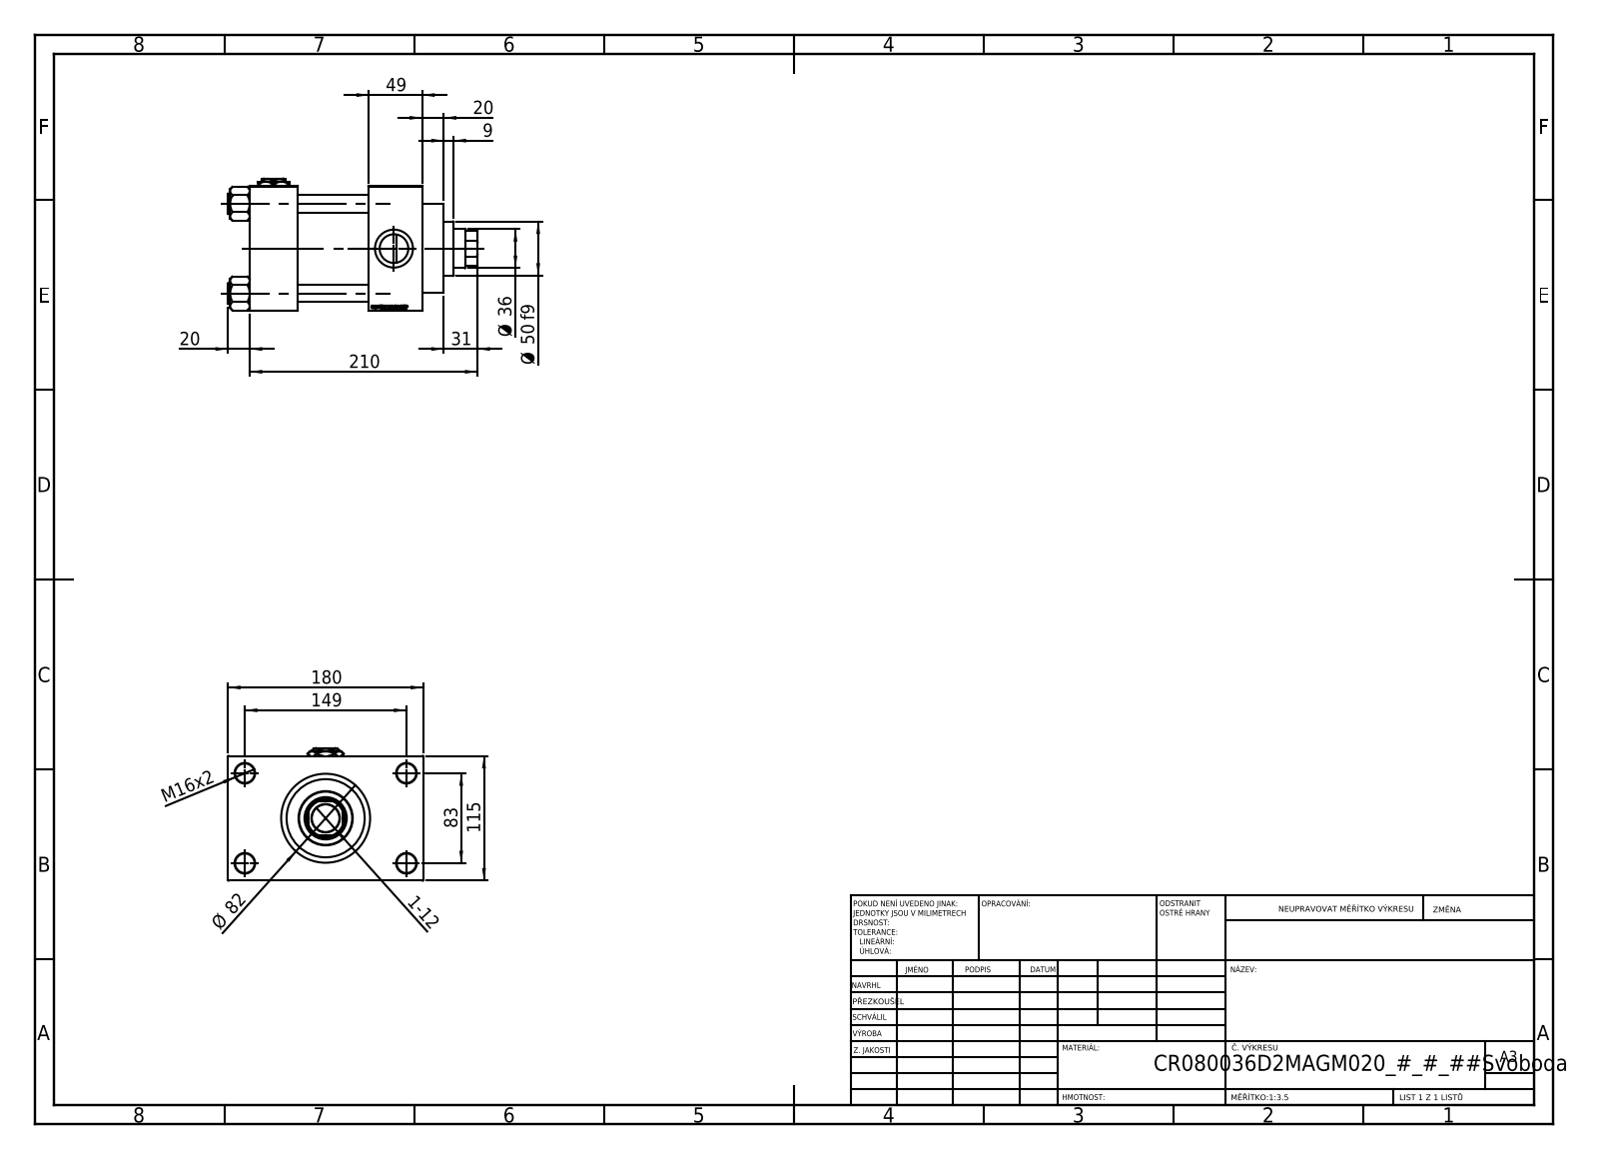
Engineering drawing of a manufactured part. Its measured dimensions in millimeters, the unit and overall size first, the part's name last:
Units: millimetres
Overall size (bounding box): 230 × 180 × 122
Round holes (diameter × count): ⌀16 ×4, ⌀18 ×4, ⌀7 ×2, ⌀26.44 ×2, ⌀35 ×2, ⌀25.5 ×1, ⌀36 ×1, ⌀39 ×1, ⌀61 ×1, ⌀72 ×1, ⌀80 ×1
Round bosses / shafts (diameter × count): ⌀19 ×4, ⌀86 ×1, ⌀82 ×1, ⌀50 ×1
Partial cylindrical surfaces — rounded edges, fillets, slot ends (radius × count): R17.5 ×1
Main face-to-face distances: 115, 66, 110, 49, 44, 159, 32.5, 147.5, 20, 69
Hole centre spacings: 33.15, 58.48, 82.7, 85.28, 89.24, 115.85, 142.43, 83
Volume: 1 983 000 mm³ · Surface area: 298 618 mm²
Bodies: 12 solids, 1194 faces (567 planar, 89 cylindrical, 538 other)
Part name (STEP PRODUCT): V215CR_D_Body; NUT_M5_D; V215_VC_A; V215CR_VCP_D (+2 more)
STEP written by: SolidWorks 2019 (CONFIG_CONTROL_DESIGN)
